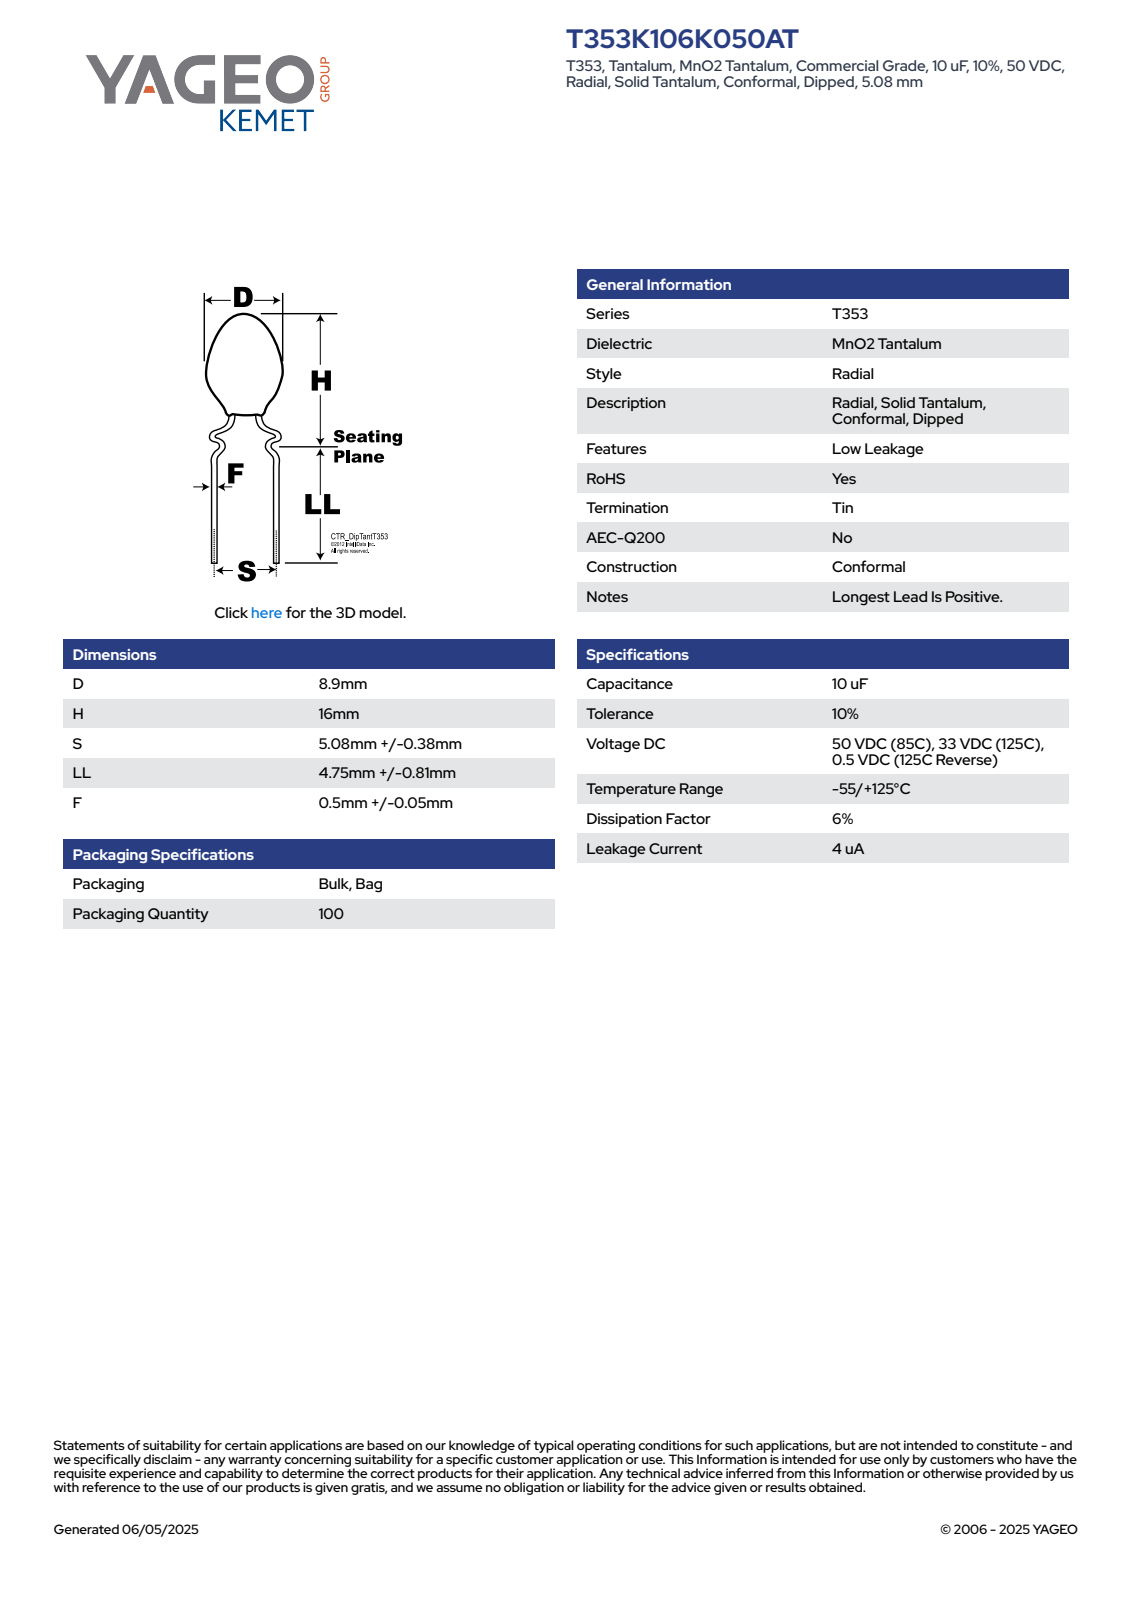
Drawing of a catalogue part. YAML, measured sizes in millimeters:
part_name: "CTR_T353_D8.9H16S5.08LL5.56F0.55"
step_written_by: "SolidWorks 2014 (AUTOMOTIVE_DESIGN)"
units: millimeters
bodies: {solids: 1, faces: 89, planar: 29, cylindrical: 10, other: 50}
overall_size: [21.56, 8.9, 8.9]
volume: 559
surface_area: 375
round_bosses_or_shafts:
  - {diameter: 0.55, count: 2}
  - {diameter: 8.9, count: 1}
partial_cylinders:
  - {radius: 4.44, count: 1}
face_to_face_distances: [10.98, 10.58, 21.56, 16.69, 6.11, 4.87, 15.68, 5.1, 1.01, 5.88]
